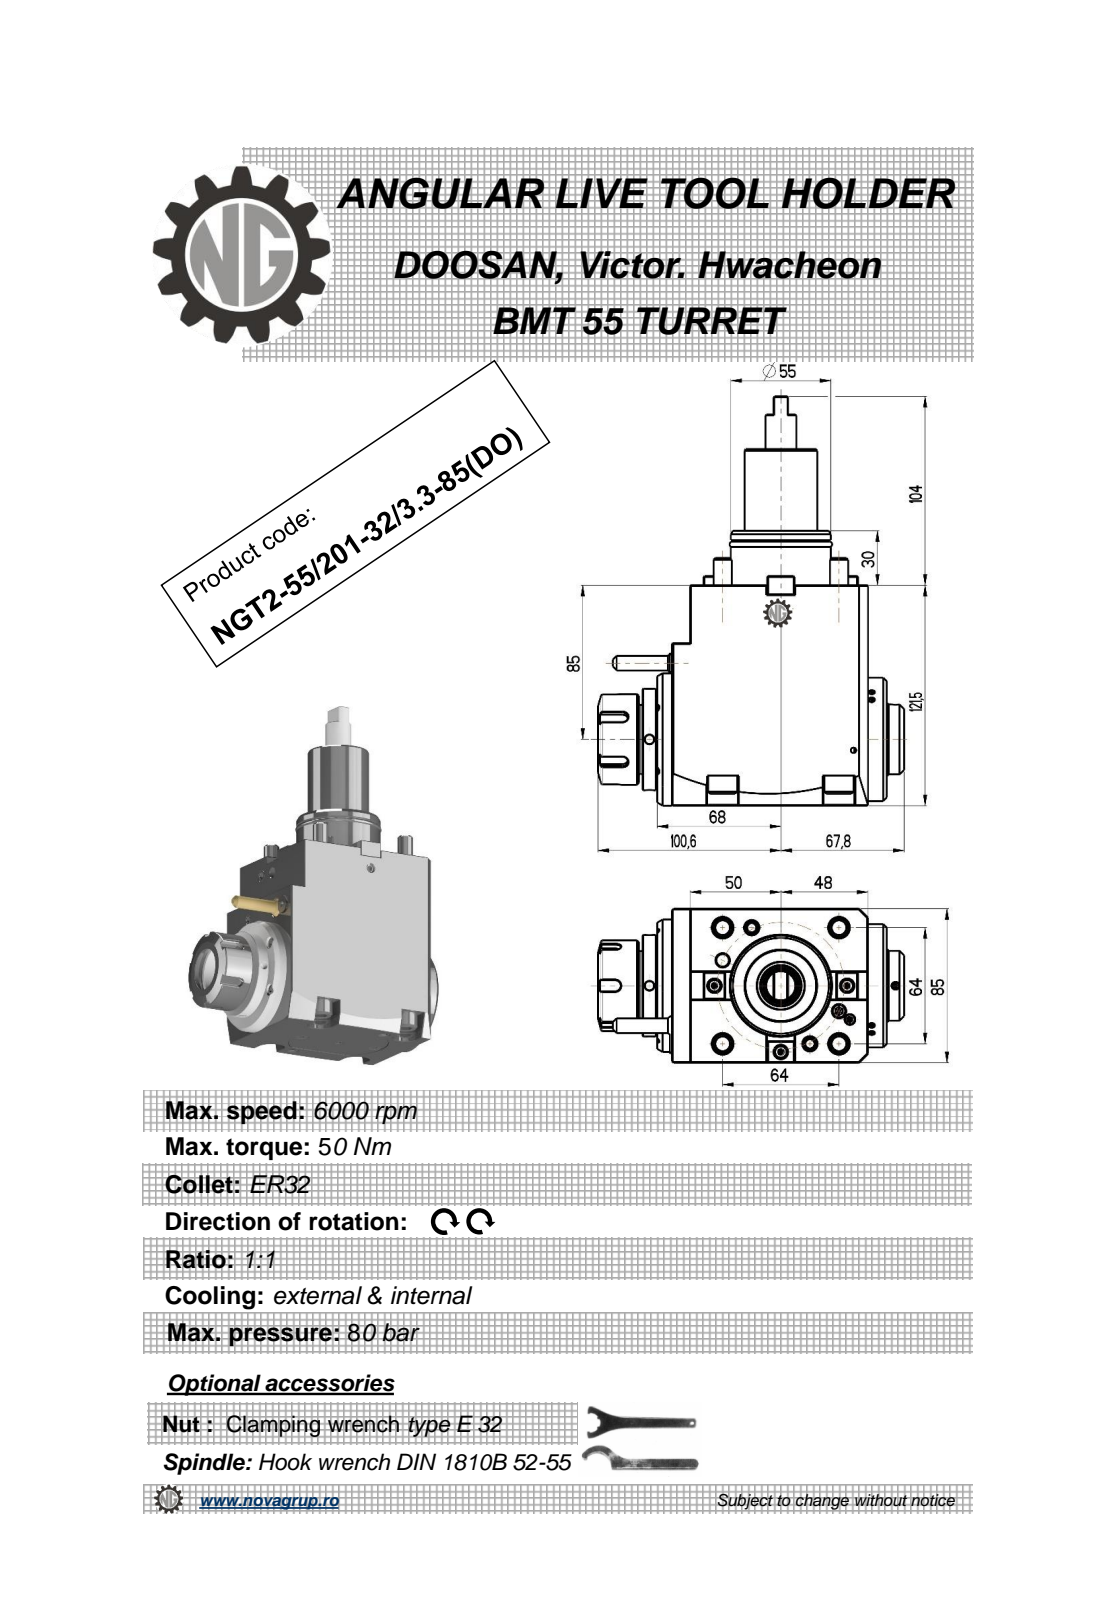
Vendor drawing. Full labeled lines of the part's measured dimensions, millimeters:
Part name (STEP PRODUCT): NGT2_55_201_32_3_3_85_DO
STEP written by: PRO/ENGINEER BY PARAMETRIC TECHNOLOGY CORPORATION, 2010280 (CONFIG_CONTROL_DESIGN)
Units: millimetres
Bodies: 2 solids, 502 faces (242 planar, 119 cylindrical, 141 other)
Overall size (bounding box): 225.5 × 168.4 × 85
Volume: 1 340 000 mm³ · Surface area: 116 281 mm²
Round holes (diameter × count): ⌀5 ×3, ⌀6.8 ×2, ⌀3 ×1, ⌀12 ×1, ⌀27 ×1
Round bosses / shafts (diameter × count): ⌀16 ×4, ⌀10 ×4, ⌀50 ×2, ⌀73 ×1, ⌀68 ×1, ⌀56 ×1, ⌀55 ×1, ⌀43.4 ×1
Partial cylindrical surfaces — rounded edges, fillets, slot ends (radius × count): R0.32 ×20, R0.22 ×6, R0.31 ×6, R3 ×5, R8.5 ×4, R0.8 ×2, R480 ×2
Main face-to-face distances: 85, 121.5, 8, 10, 108, 18, 98, 116, 108.3, 126.3
Hole centre spacings: 42.62, 47.41, 69.86, 105.19
